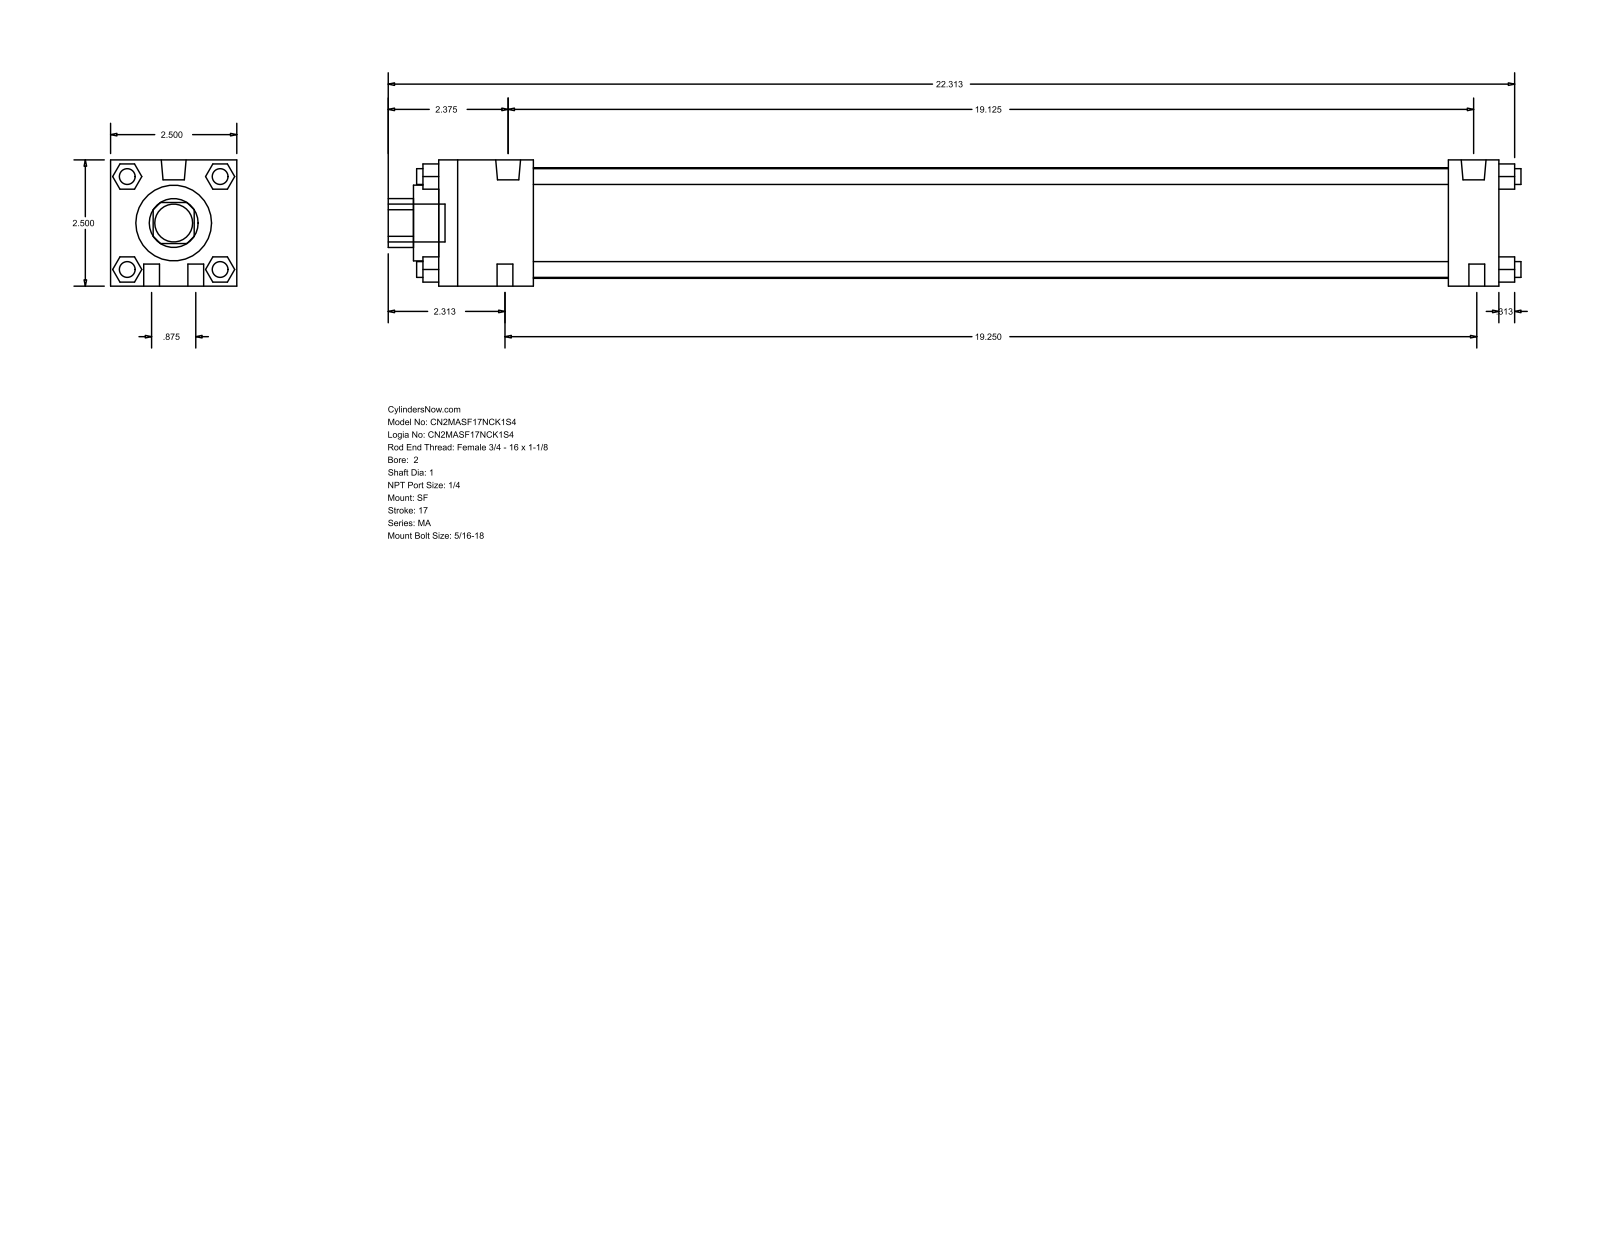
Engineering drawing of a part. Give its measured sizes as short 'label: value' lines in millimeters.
name: MA_SF__0200_1
written by: GSSL Pune (CONFIG_CONTROL_DESIGN)
unit: mm
bodies: 0 solids, 124 faces (94 planar, 30 cylindrical, 0 other)
size: 569.91 × 63.5 × 63.5
holes: 1× ⌀25.4, 1× ⌀38.1, 1× ⌀55.63
bosses: 10× ⌀7.94, 2× ⌀12.49, 1× ⌀19.05
rounds: 1× R12.29
face distances: 63.5, 533.4, 12.7, 25.4, 508, 47.63, 460.37, 485.77, 23.37, 40.47
